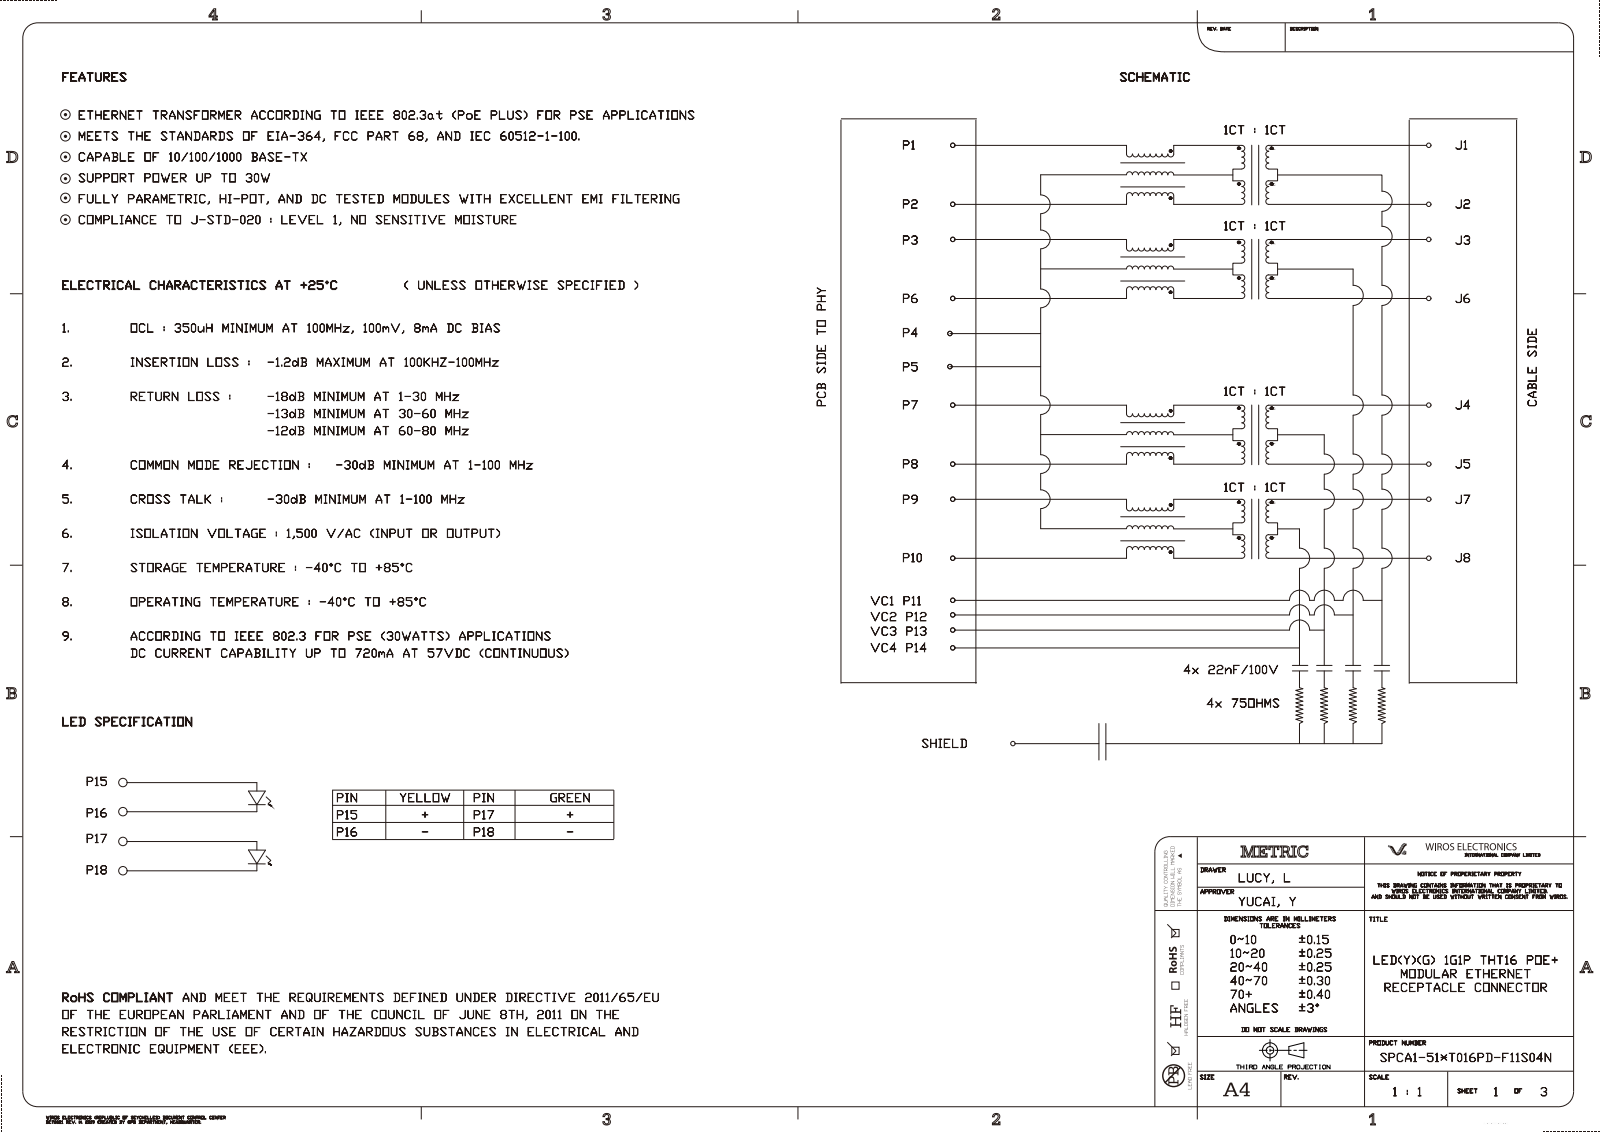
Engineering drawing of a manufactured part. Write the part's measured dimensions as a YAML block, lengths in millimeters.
part_name: "XWRJ-1108F1016"
step_written_by: "PRO/ENGINEER BY PARAMETRIC TECHNOLOGY CORPORATION, 2010280 (CONFIG_CONTROL_DESIGN)"
units: millimeters
bodies: {solids: 1, faces: 542, planar: 425, cylindrical: 111, other: 6}
overall_size: [21.25, 17.55, 16.35]
volume: 3022
surface_area: 3132
partial_cylinders:
  - {radius: 0.3, count: 12}
  - {radius: 1.16, count: 8}
  - {radius: 0.4, count: 5}
  - {radius: 0.1, count: 4}
  - {radius: 0.2, count: 3}
  - {radius: 0.12, count: 2}
  - {radius: 0.15, count: 2}
  - {radius: 0.37, count: 2}
face_to_face_distances: [13.3, 15.94, 2.71, 10.59, 2.02, 13.92, 6.25, 10.79, 0.46, 1.56]
